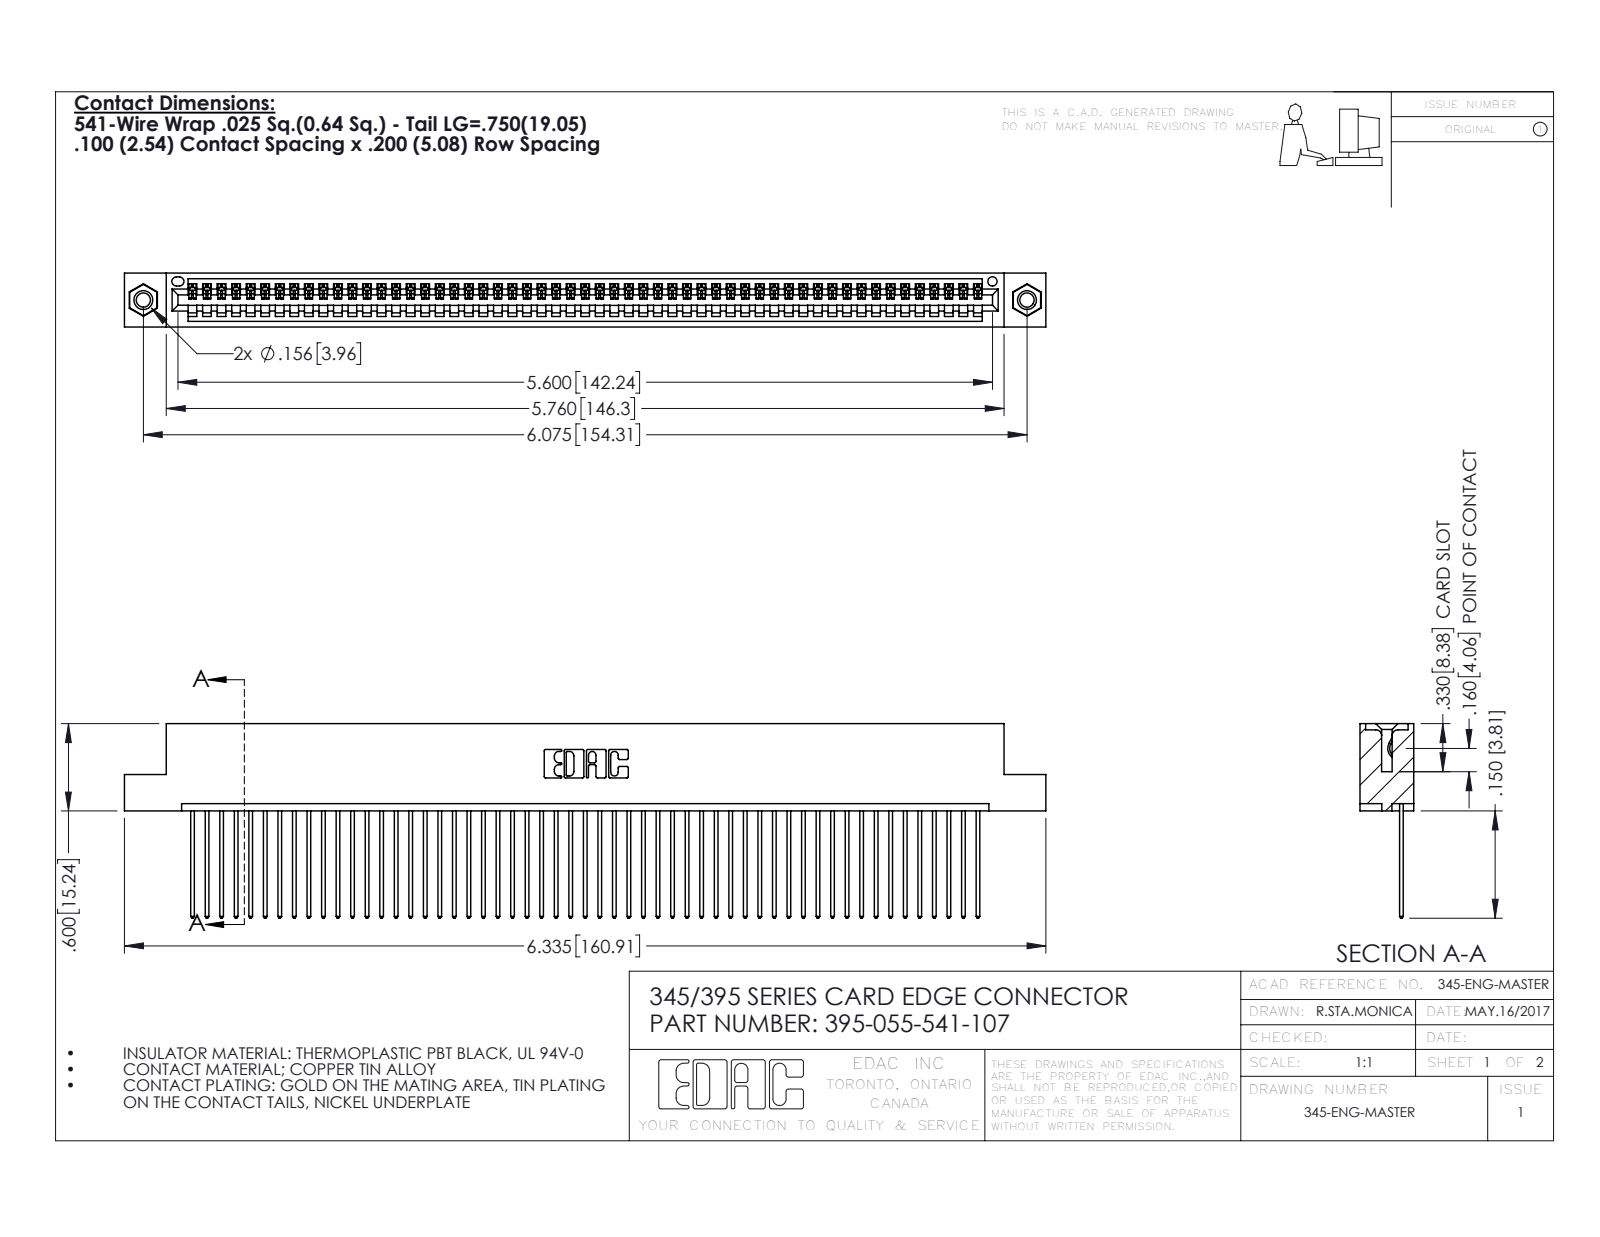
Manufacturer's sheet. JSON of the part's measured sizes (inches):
{"part_name": "395-055-541-107; 345-292-001_345-293-141; 345 Part_Flush Mounting Lugs - 0.156 Dia-TI; 345-250-001_345-250-005-103", "step_written_by": "SolidWorks 2016 (CONFIG_CONTROL_DESIGN)", "units": "inches", "bodies": {"solids": 58, "faces": 3376, "planar": 2312, "cylindrical": 1048, "other": 16}, "overall_size": [6.335, 1.337, 0.37], "volume_in3": 0.949, "surface_area_in2": 34.03, "round_holes": [[0.098, 2], [0.125, 2], [0.156, 2], [0.064, 1]], "round_bosses_or_shafts": [[0.155, 2]], "partial_cylinders_radius": [[0.006, 110], [0.01, 110], [0.01, 22], [0.007, 6], [0.031, 6], [0.026, 3], [0.031, 2], [0.04, 2]], "face_to_face_distances": [0.072, 0.298, 0.098, 0.272, 0.025, 0.37, 0.2, 0.225, 0.149, 0.072], "hole_center_spacings": [0.27, 5.839, 6.075]}
